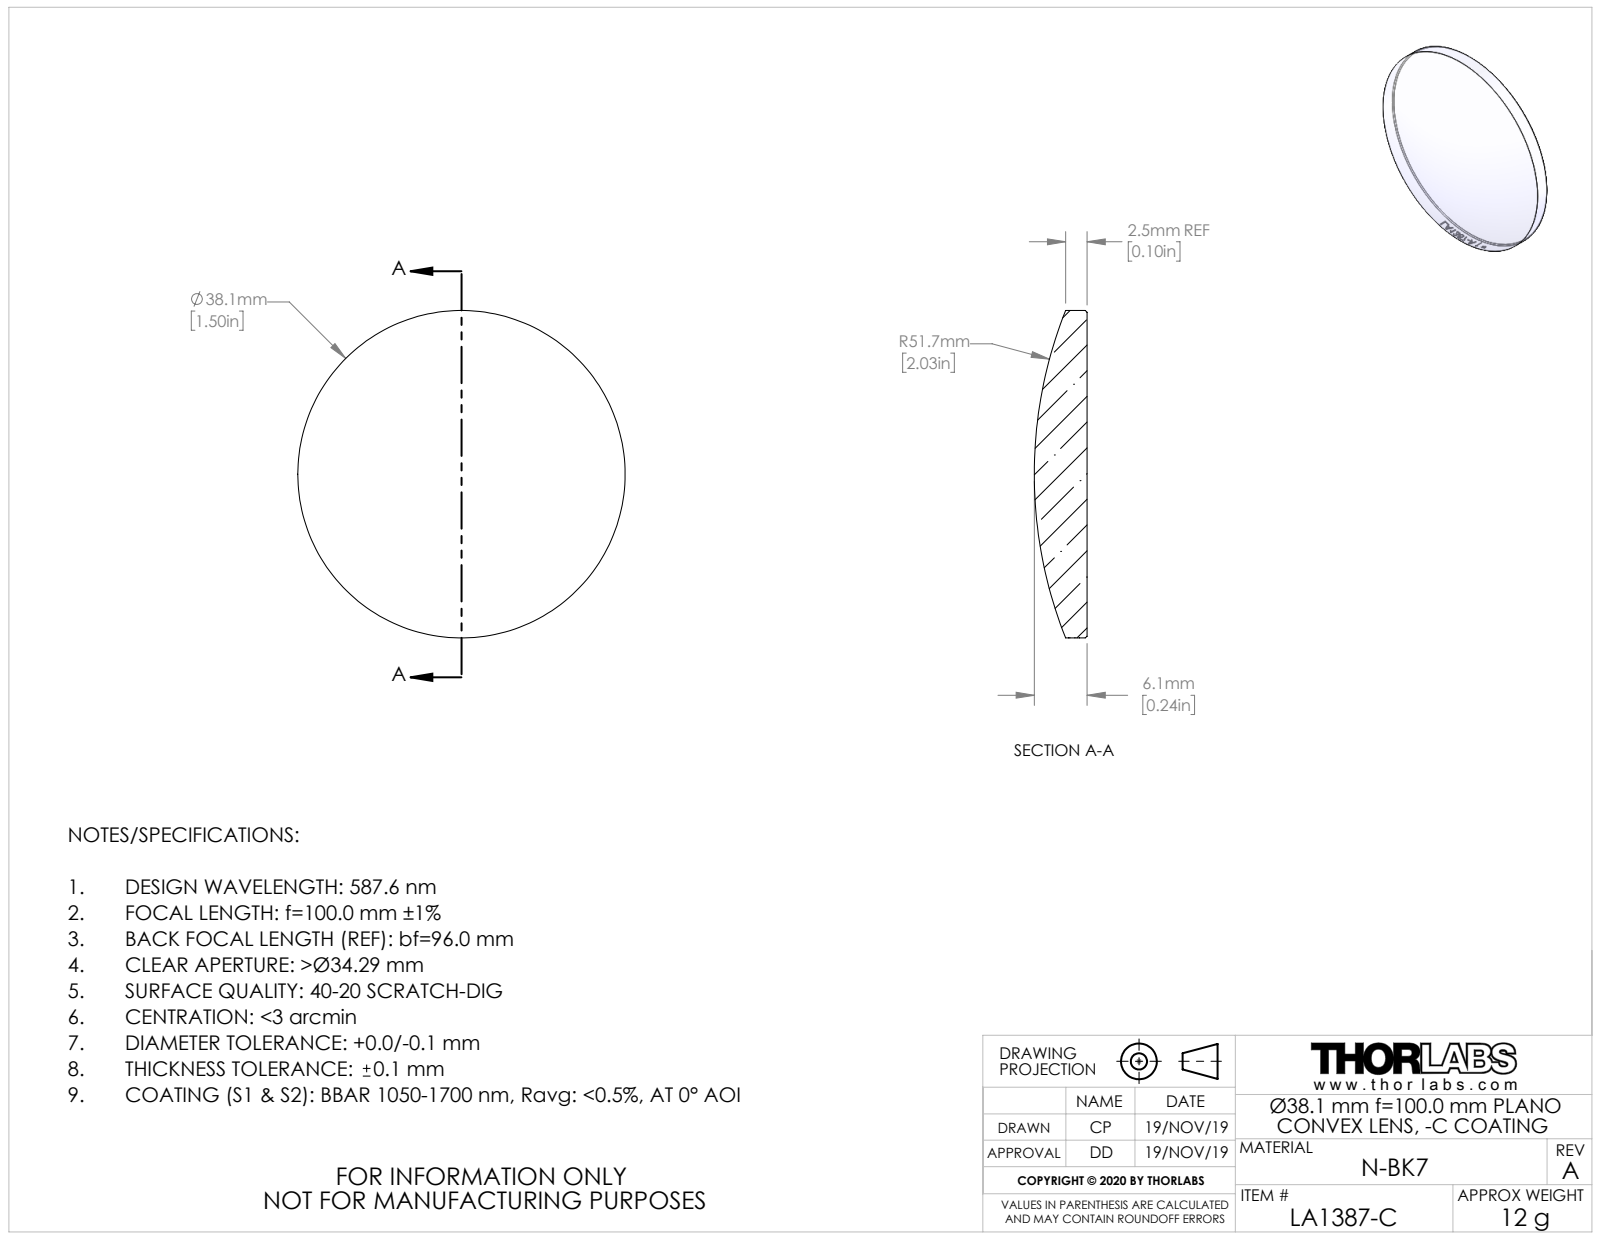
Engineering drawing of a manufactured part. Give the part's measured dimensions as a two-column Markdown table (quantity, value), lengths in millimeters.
| quantity | value |
| --- | --- |
| part name | TTN200740-E0W |
| STEP written by | SolidWorks 2018 (CONFIG_CONTROL_DESIGN) |
| units | millimeters |
| bodies | 1 solid, 23 faces (1 planar, 18 cylindrical, 4 other) |
| overall size | 38.1 × 38.1 × 6.14 |
| volume | 4 949 mm³ |
| surface area | 2 607 mm² |
| round bosses / shafts (diameter × count) | 38.1 × 1 |
